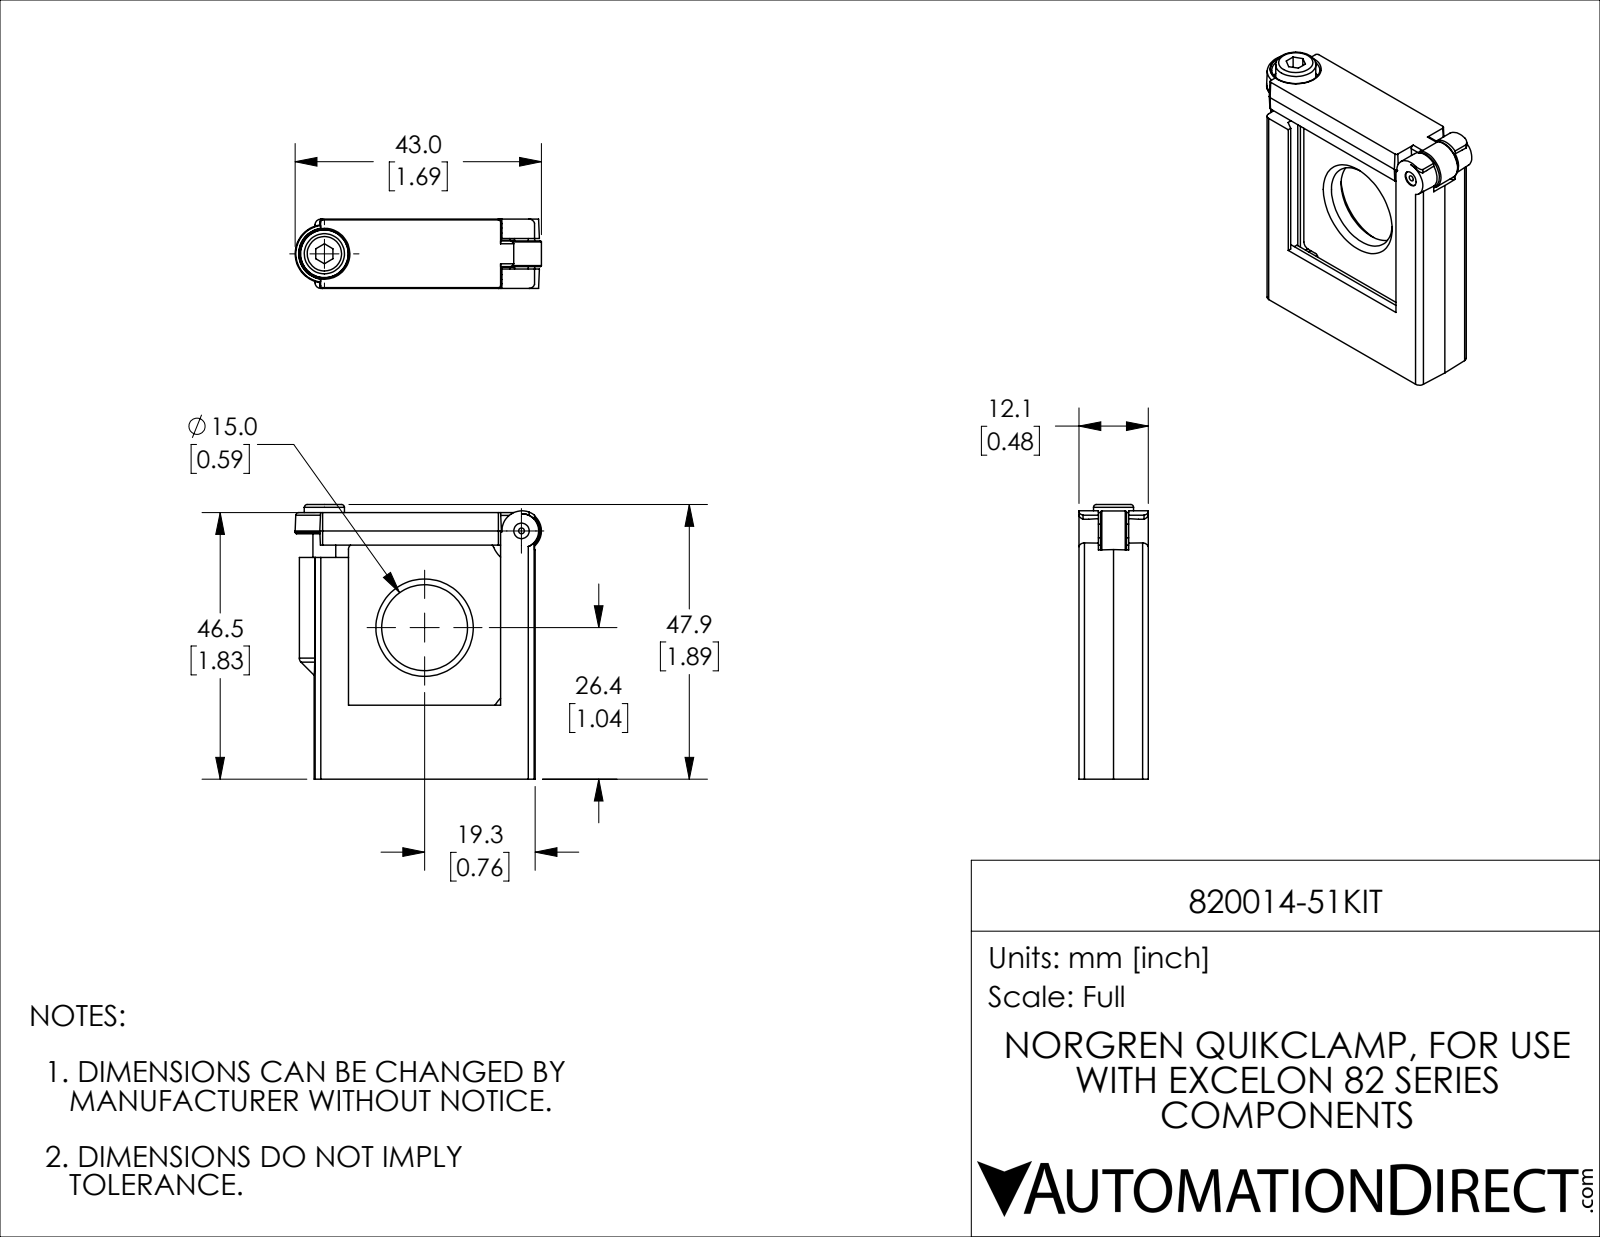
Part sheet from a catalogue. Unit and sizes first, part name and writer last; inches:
Units: inches
Overall size (bounding box): 1.887 × 1.693 × 0.476
Round holes (diameter × count): ⌀0.039 ×1, ⌀0.106 ×1, ⌀0.128 ×1, ⌀0.175 ×1, ⌀0.187 ×1, ⌀0.591 ×1
Round bosses / shafts (diameter × count): ⌀0.276 ×1, ⌀0.274 ×1, ⌀0.157 ×1, ⌀0.094 ×1
Partial cylindrical surfaces — rounded edges, fillets, slot ends (radius × count): R0.039 ×22, R0.02 ×6, R0.03 ×6, R0.175 ×2, R0.118 ×1, R0.138 ×1, R0.157 ×1, R0.172 ×1
Main face-to-face distances: 0.152, 0.325, 0.476, 0.173, 0.224, 1.518, 1.831, 0.146, 1.607, 0.476
Hole centre spacings: 0.689, 0.941
Volume: 0.752 in³ · Surface area: 14.12 in²
Bodies: 1 solid, 239 faces (123 planar, 67 cylindrical, 49 other)
Part name (STEP PRODUCT): 820014-51KIT
STEP written by: SolidWorks 2021 (CONFIG_CONTROL_DESIGN)
